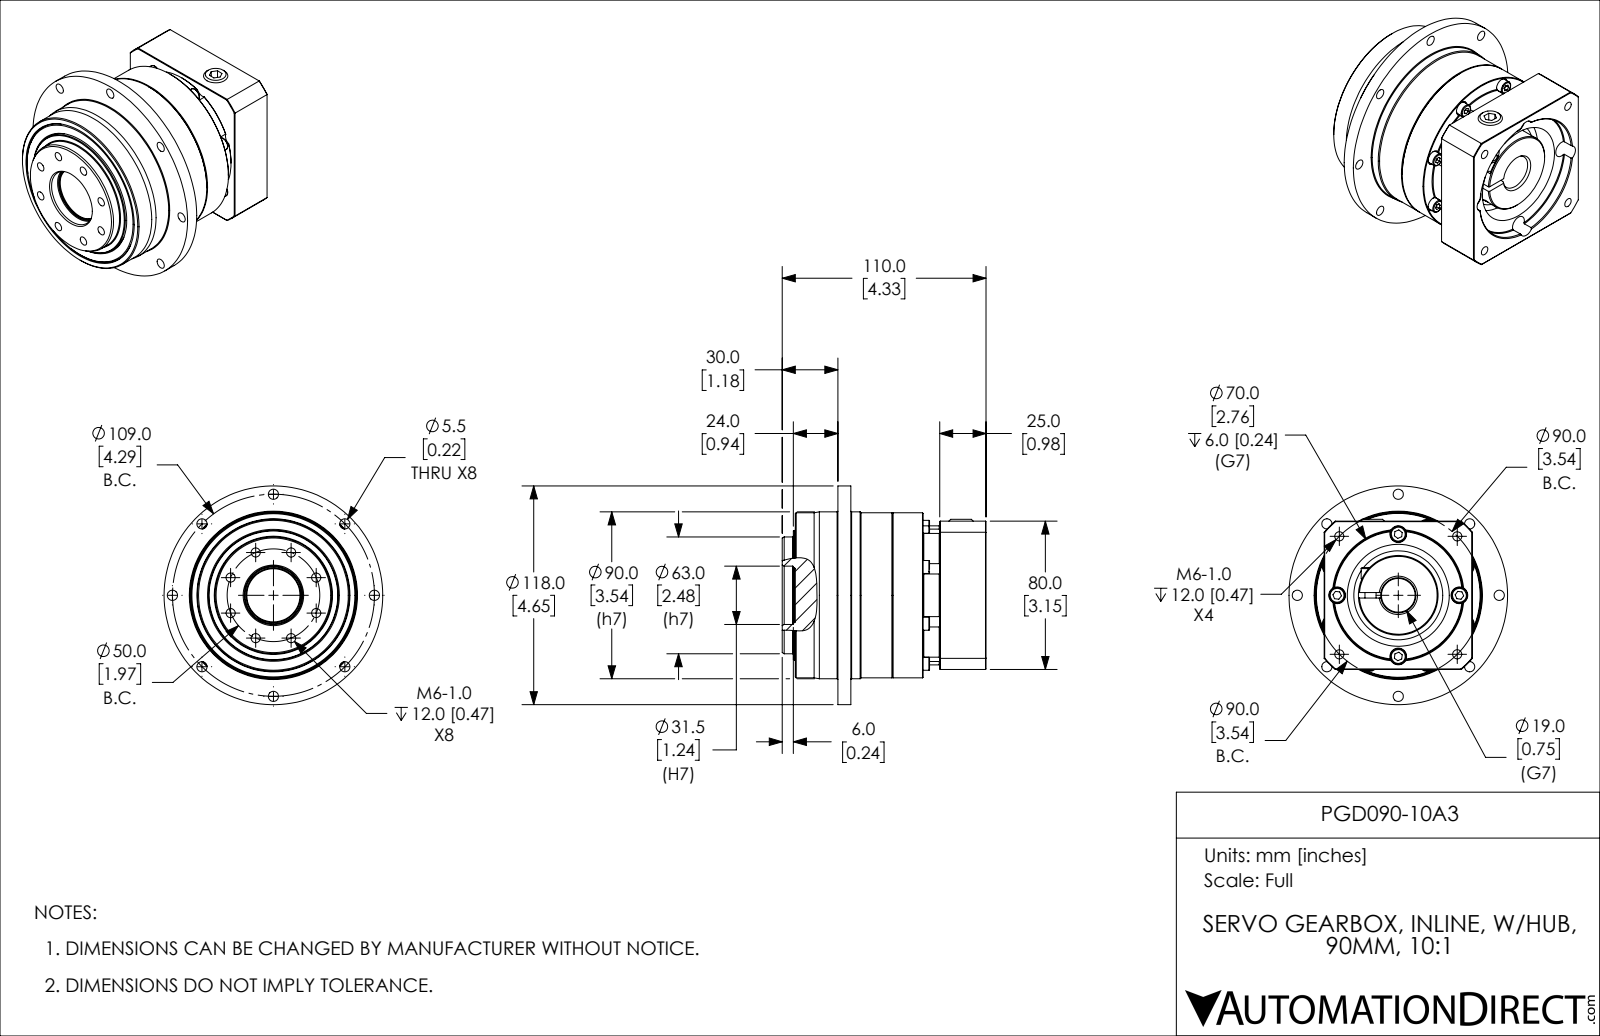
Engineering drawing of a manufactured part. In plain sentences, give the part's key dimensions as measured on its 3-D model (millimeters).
The part is named "PGD090-10A3". Its 3-D file was written by "SolidWorks 2015 (AUTOMOTIVE_DESIGN)". It is 5 solids with 496 faces: 253 planar, 160 cylindrical and 83 other. Overall it measures 118 by 118 by 110 millimeters. Its volume is 605 353 cubic millimeters and its surface area 81 344 square millimeters. Round holes: 9 of diameter 4.92, 8 of diameter 5.5, 4 of diameter 9, 3 of diameter 4.92, 3 of diameter 6, 1 of diameter 5, 1 of diameter 9.6, 1 of diameter 10, 1 of diameter 18, 1 of diameter 19, 1 of diameter 20, 1 of diameter 31.5. Round bosses or shafts: 9 of diameter 7, 4 of diameter 8.5, 1 of diameter 118, 1 of diameter 90, 1 of diameter 89, 1 of diameter 65, 1 of diameter 63, 1 of diameter 42. Partial cylindrical surfaces (rounded edges, fillets, slot ends): 1 of radius 5.5, 1 of radius 19.5, 1 of radius 34.6, 1 of radius 35, 1 of radius 52.5. The main face-to-face distances are 80, 4, 23, 74, 27, 11, 30, 19, 51, 55. The hole center spacings are 32.83, 68.11, 78.19, 25, 13.77, 23.9, 31.84, 32.9.
